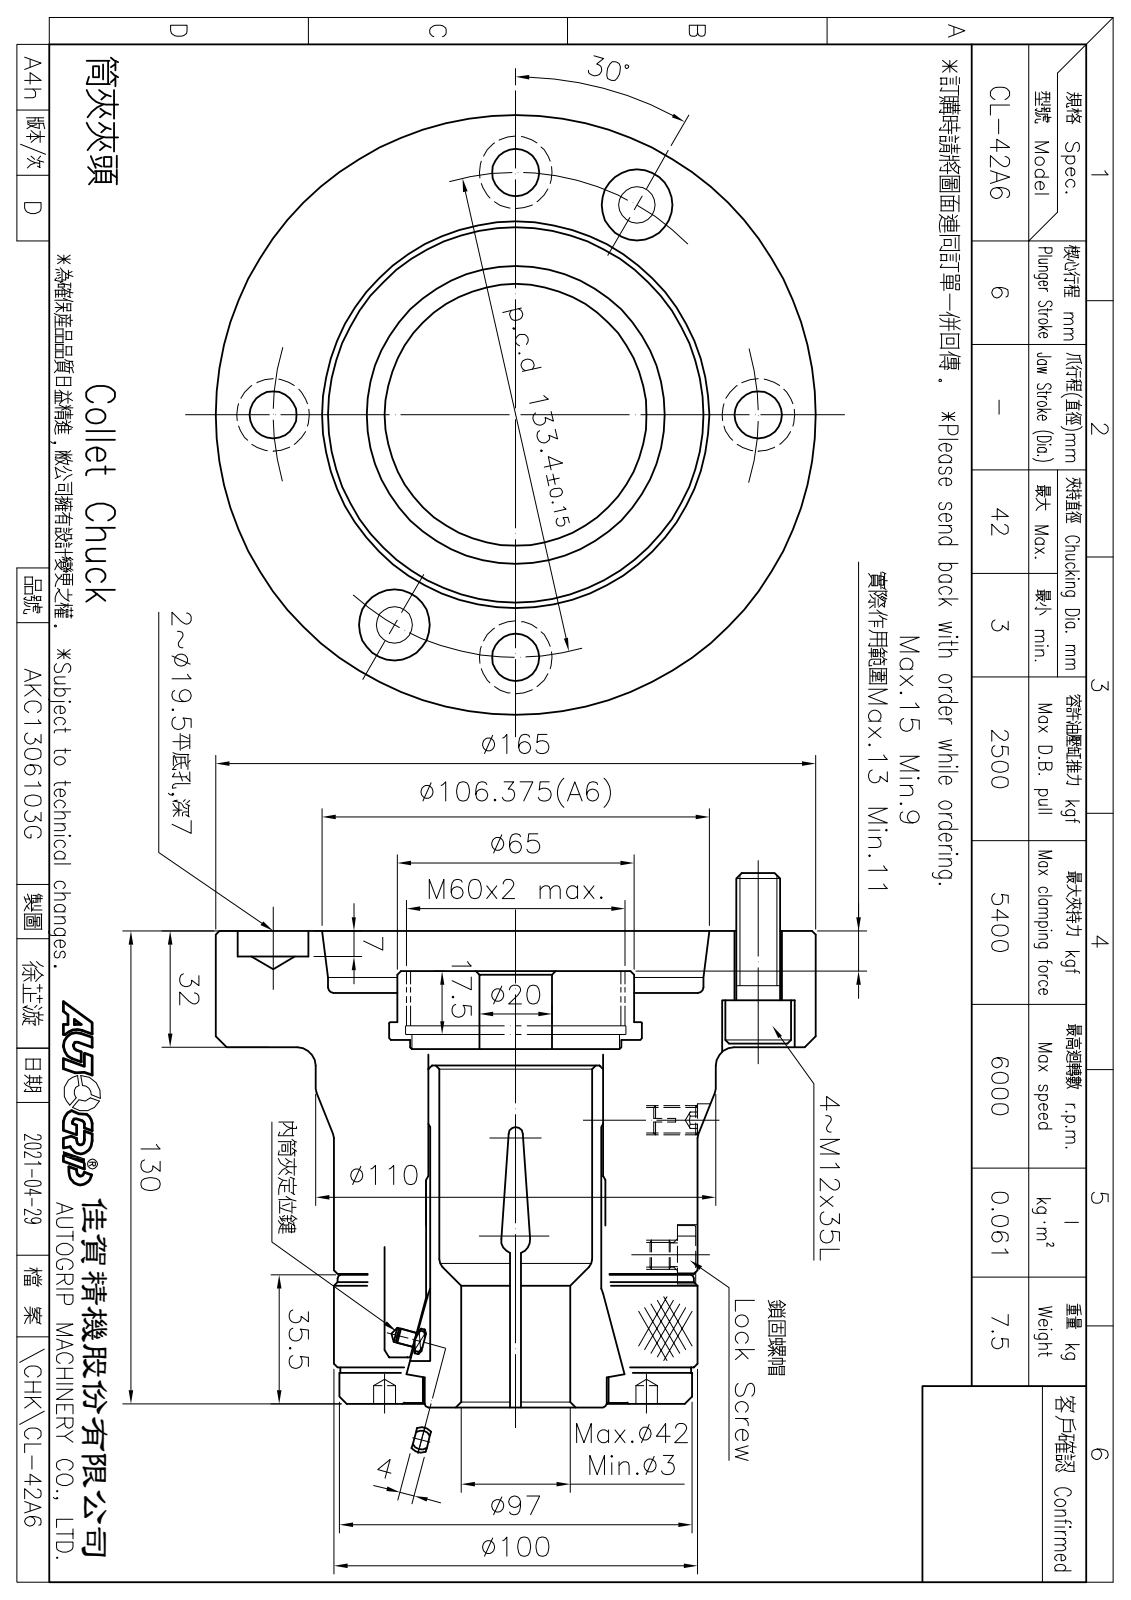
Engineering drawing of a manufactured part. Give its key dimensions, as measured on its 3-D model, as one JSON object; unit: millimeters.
{"part_name": "CF-CL-42A6-02010; CF-CL-42A6-04000; 圓頭內六角螺栓_M12x35; CF-CL-42-11000 (+4 more)", "step_written_by": "SolidWorks 2016 (CONFIG_CONTROL_DESIGN)", "units": "millimeters", "bodies": {"solids": 10, "faces": 342, "planar": 113, "cylindrical": 115, "other": 114}, "overall_size": [165, 165, 145.72], "volume_mm3": 1079000, "surface_area_mm2": 209758, "round_holes": [[13.5, 4], [20, 4], [6, 2], [19.5, 2], [4, 1], [6.8, 1], [43, 1], [48, 1], [49.3, 1], [51, 1], [58, 1], [60.5, 1]], "round_bosses_or_shafts": [[18, 4], [12, 4], [165, 1], [110, 1], [100, 1], [98, 1], [97, 1], [96.4, 1]], "partial_cylinders_radius": [[8.5, 3], [3.5, 1], [8, 1], [8.25, 1]], "face_to_face_distances": [32, 130, 98, 9.5, 28.02, 3.98, 101.98, 17, 11.02, 15], "hole_center_spacings": [66.7, 94.33, 34.53, 36, 39.82, 57.83, 75.79, 75.8]}
